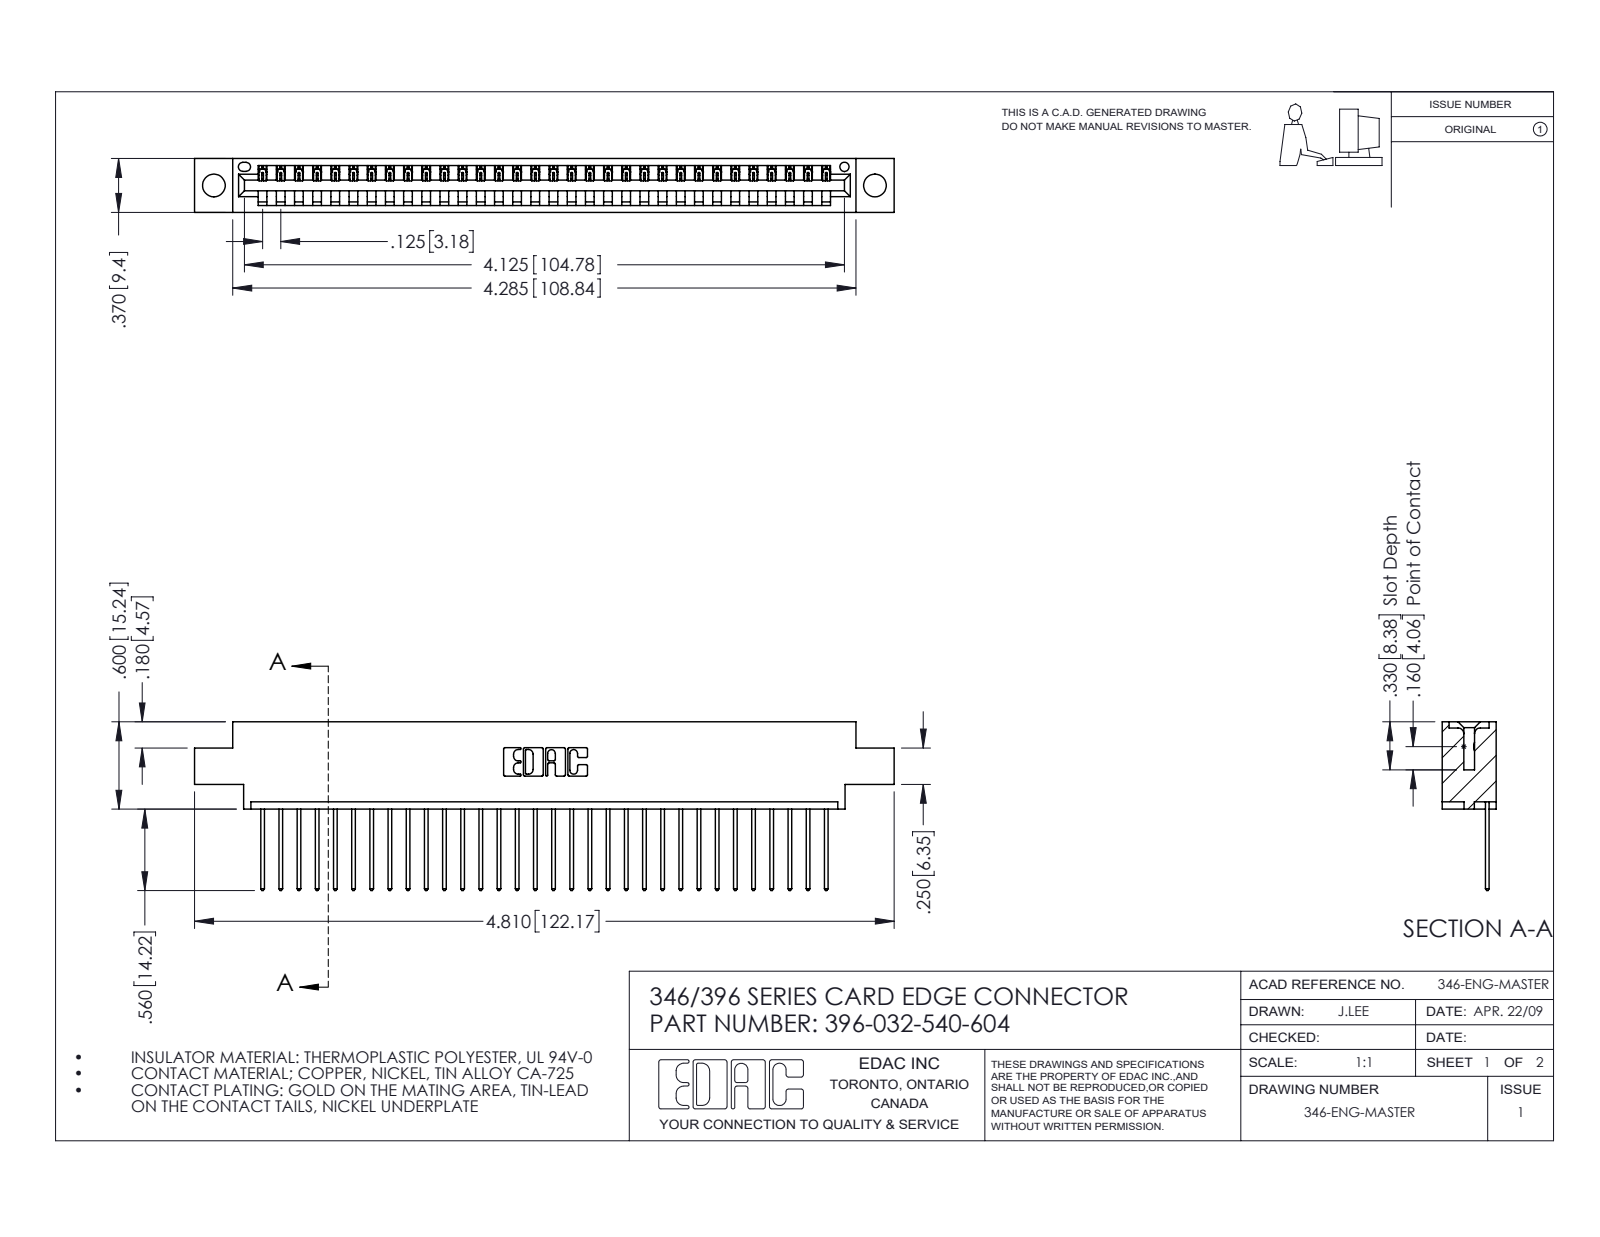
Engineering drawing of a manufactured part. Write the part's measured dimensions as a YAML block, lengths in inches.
part_name: "396-032-540-604; 345-292-001_345-293-140; 346 Part_0.170 Offset - 0.156 Dia-TH"
step_written_by: "SolidWorks 2016 (CONFIG_CONTROL_DESIGN)"
units: inches
bodies: {solids: 33, faces: 1982, planar: 1360, cylindrical: 622, other: 0}
overall_size: [4.81, 1.16, 0.37]
volume: 0.697
surface_area: 22.41
round_holes:
  - {diameter: 0.156, count: 2}
  - {diameter: 0.064, count: 1}
partial_cylinders:
  - {radius: 0.006, count: 64}
  - {radius: 0.01, count: 64}
  - {radius: 0.01, count: 22}
  - {radius: 0.007, count: 6}
  - {radius: 0.031, count: 6}
  - {radius: 0.026, count: 3}
  - {radius: 0.031, count: 2}
  - {radius: 0.04, count: 2}
face_to_face_distances: [0.048, 0.322, 0.37, 0.25, 0.072, 0.298, 0.025, 0.148, 0.222, 0.1]
hole_center_spacings: [0.246, 4.337, 4.545]
